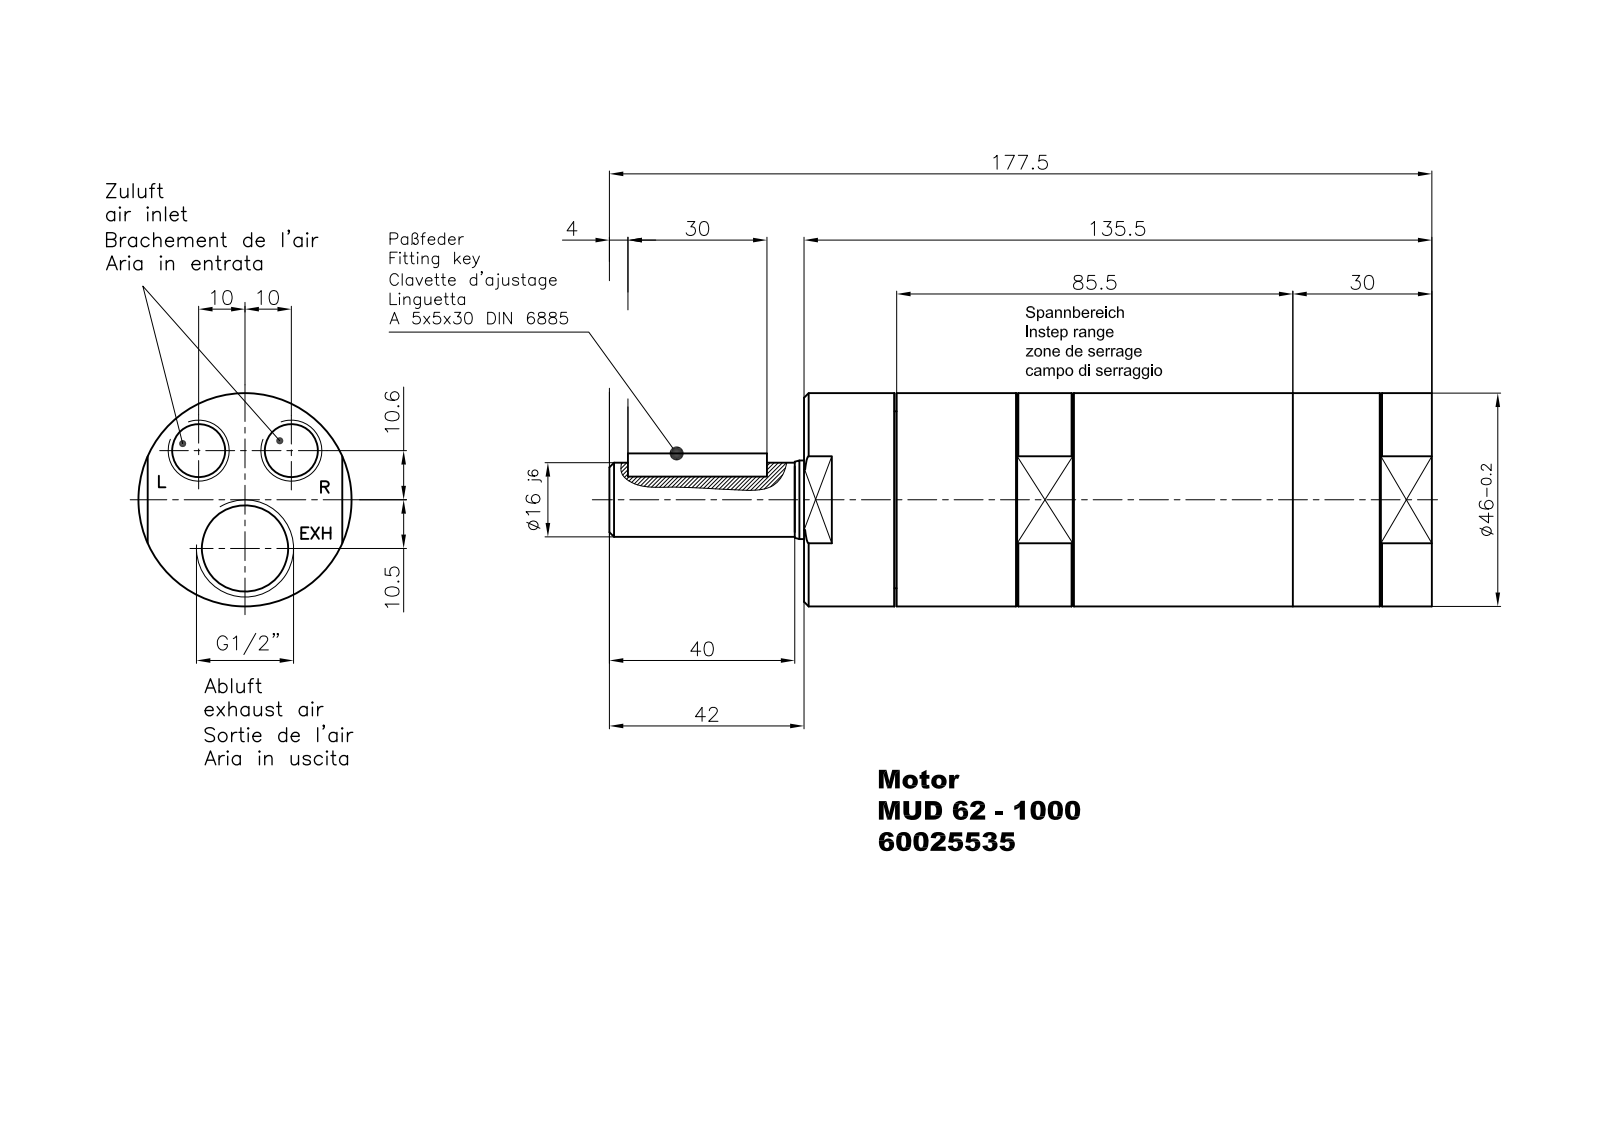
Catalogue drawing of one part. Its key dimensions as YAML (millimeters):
part_name: "MUD 62-177"
step_written_by: "Autodesk Inventor 2012 (AUTOMOTIVE_DESIGN)"
units: millimeters
bodies: {solids: 1, faces: 135, planar: 92, cylindrical: 18, other: 25}
overall_size: [177.5, 46, 46]
volume: 225154
surface_area: 28631
round_holes:
  - {diameter: 11.45, count: 2}
  - {diameter: 1.6, count: 1}
  - {diameter: 17.5, count: 1}
  - {diameter: 18.63, count: 1}
round_bosses_or_shafts:
  - {diameter: 46, count: 1}
  - {diameter: 38.16, count: 1}
  - {diameter: 16.95, count: 1}
  - {diameter: 16, count: 1}
partial_cylinders:
  - {radius: 2.5, count: 2}
face_to_face_distances: [135.5, 42, 30, 105.5, 19.5, 86, 116, 115.5, 20, 0.5]
hole_center_spacings: [14.57, 23.35, 10.5, 20]
